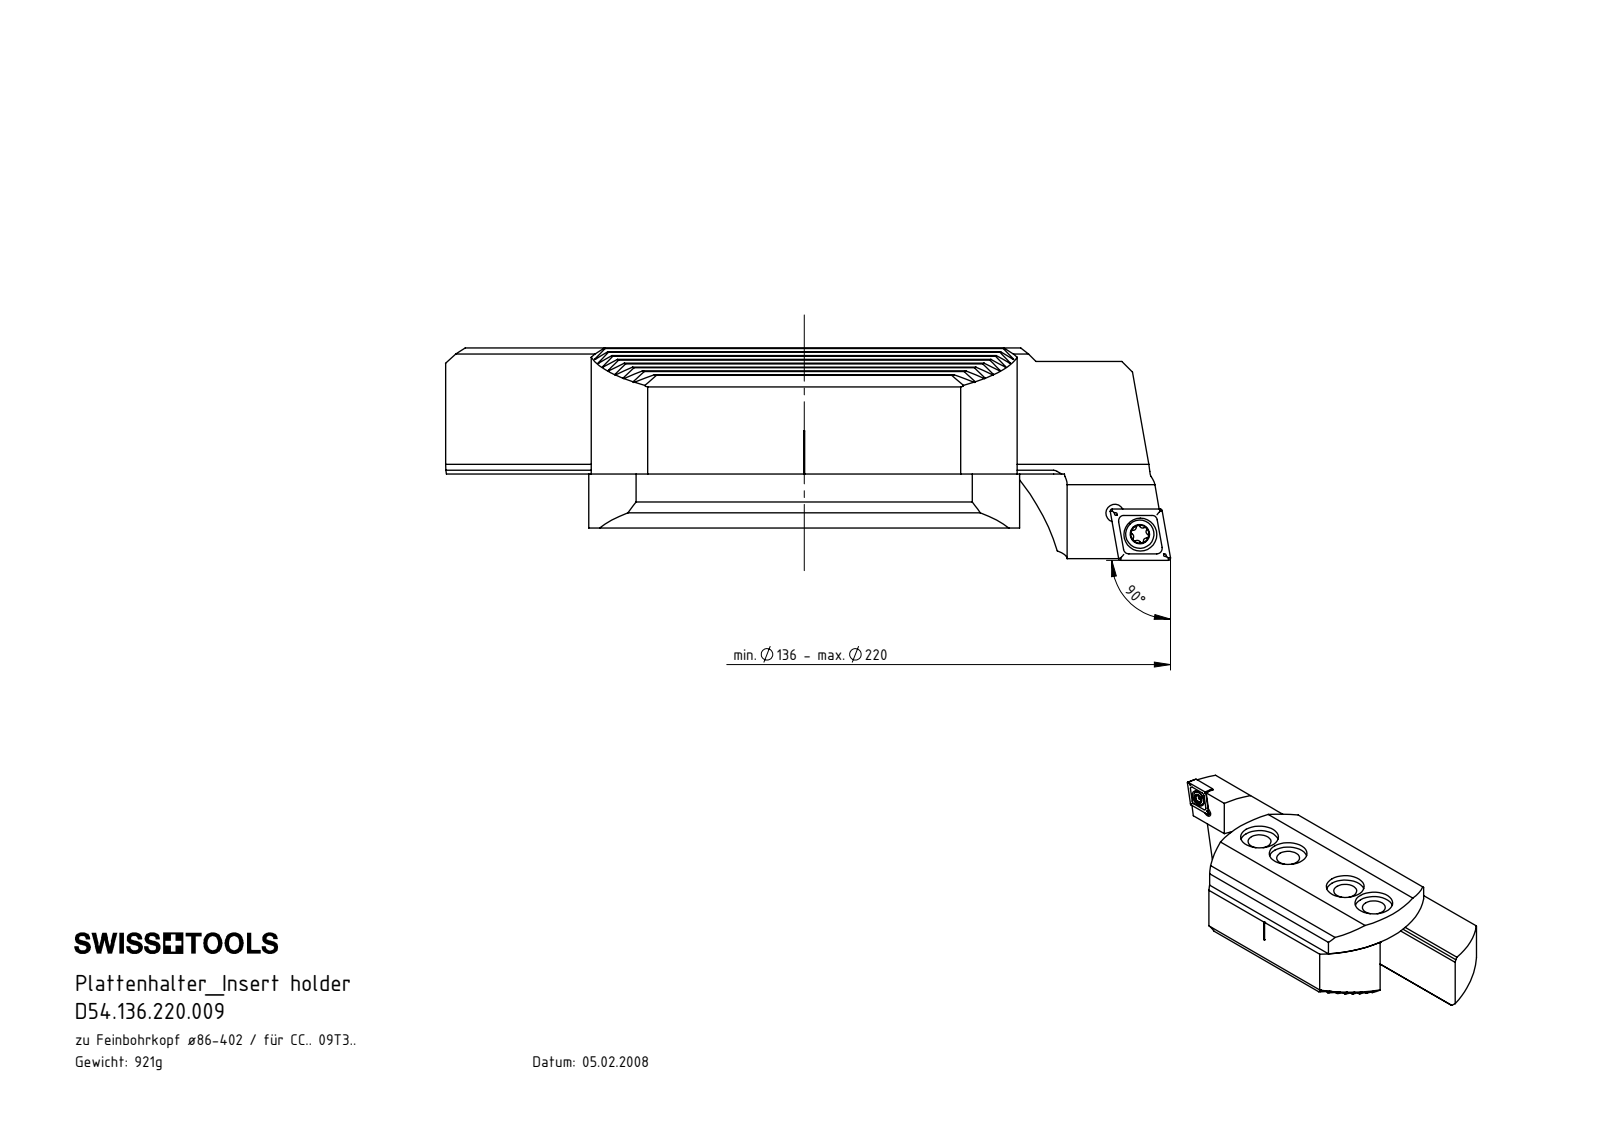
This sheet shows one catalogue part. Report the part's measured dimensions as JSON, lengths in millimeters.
{"part_name": "F00-WCB.136.001_C; CCMT09T304; D54.136.220.009; F00-WCB.136.003_B (+3 more)", "step_written_by": "SolidWorks 2017 (CONFIG_CONTROL_DESIGN)", "units": "millimeters", "bodies": {"solids": 5, "faces": 639, "planar": 386, "cylindrical": 67, "other": 186}, "overall_size": [134.57, 55, 39.4], "volume_mm3": 117330, "surface_area_mm2": 31785, "round_holes": [[8.5, 4], [14, 4], [3.3, 2], [4.4, 1], [6.1, 1]], "round_bosses_or_shafts": [[5.25, 1], [4, 1]], "partial_cylinders_radius": [[0.2, 16], [0.34, 6], [0.59, 6], [40, 6], [0.8, 1]], "face_to_face_distances": [2.38, 4.76, 21.3, 33.7, 7.14, 12.4, 9.52, 10, 9.53, 7.15], "hole_center_spacings": [15, 45, 6.06, 6.19, 30, 60]}
